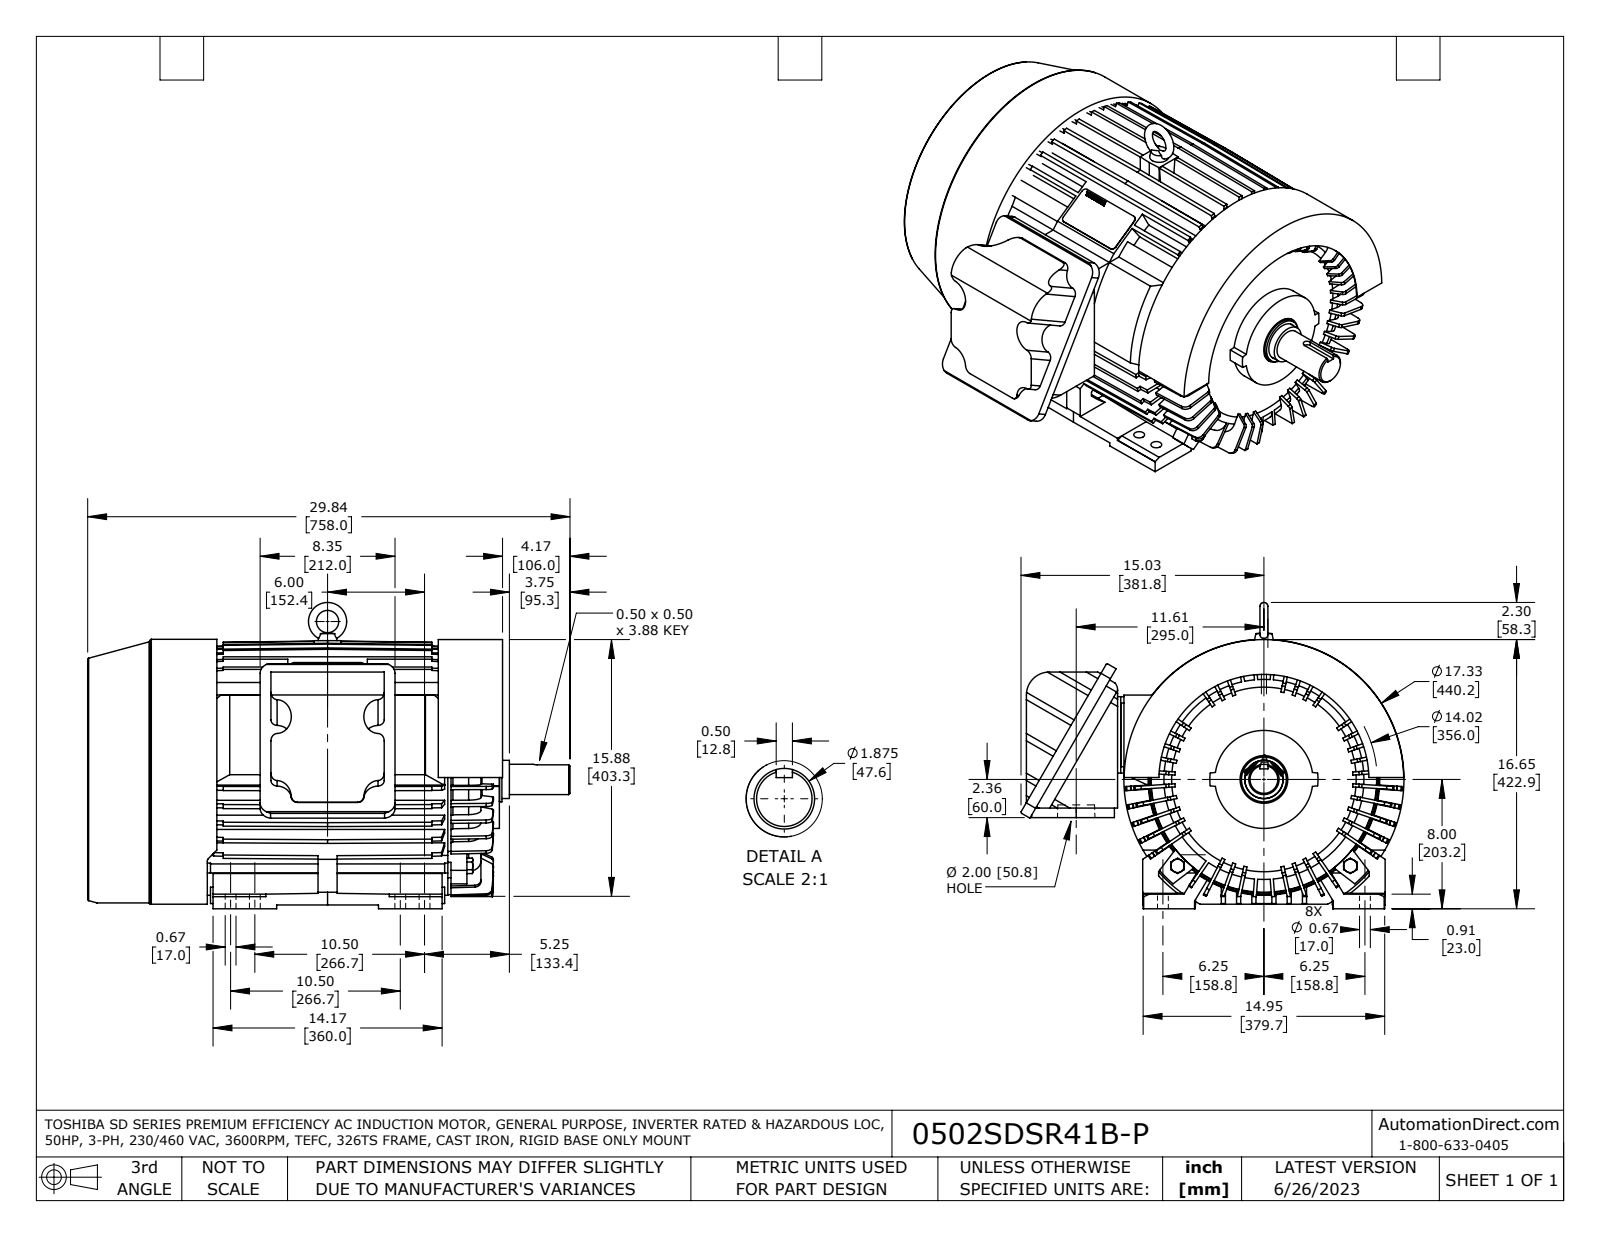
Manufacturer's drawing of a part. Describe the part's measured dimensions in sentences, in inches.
The part is named "MDSLV002-06-2P-F1-Bottom nc bod broke rep1". Its 3-D file was written by "SolidWorks 2021 (AUTOMOTIVE_DESIGN)". It is 14 solids with 3455 faces: 2632 planar, 255 cylindrical and 568 other. Overall it measures 29.843 by 23.696 by 18.945 inches. Its volume is 5 442 cubic inches and its surface area 5 263 square inches. Round holes: 8 of diameter 0.354, 8 of diameter 0.669, 4 of diameter 0.087, 4 of diameter 0.398, 4 of diameter 0.551, 2 of diameter 0.262, 1 of diameter 0.472, 1 of diameter 0.545, 1 of diameter 1.26, 1 of diameter 2.382, 1 of diameter 2.756, 1 of diameter 2.953. Round bosses or shafts: 1 of diameter 17.331, 1 of diameter 14.331, 1 of diameter 14.252, 1 of diameter 13.819, 1 of diameter 6.063, 1 of diameter 2.795, 1 of diameter 2.776, 1 of diameter 2.362. Partial cylindrical surfaces (rounded edges, fillets, slot ends): 26 of radius 0.394, 6 of radius 0.021, 6 of radius 0.042, 6 of radius 0.055, 6 of radius 0.906, 4 of radius 0.02, 4 of radius 0.09, 4 of radius 0.25. The main face-to-face distances are 0.256, 0.591, 14.882, 14.291, 14.016, 14.606, 0.276, 0.197, 0.256, 7.992. The hole center spacings are 10.228, 0.669, 1.5, 2.363, 3.341, 6.889, 7.559, 7.702.
